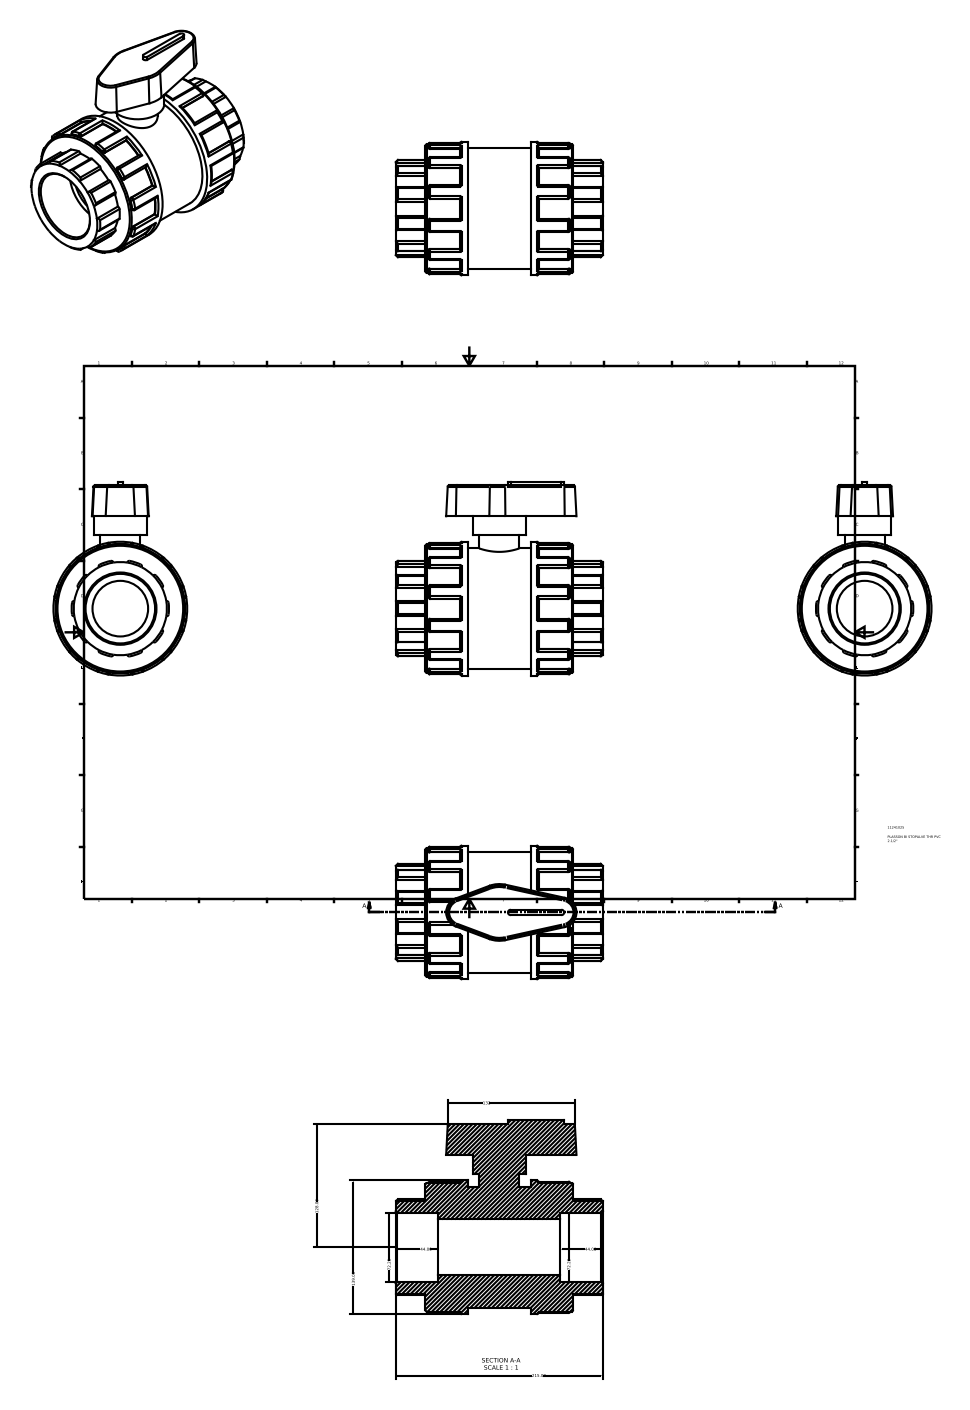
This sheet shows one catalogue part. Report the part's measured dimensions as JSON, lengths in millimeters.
{"part_name": "11241025", "step_written_by": "Autodesk Inventor 2015 (AUTOMOTIVE_DESIGN)", "units": "millimeters", "bodies": {"solids": 1, "faces": 434, "planar": 114, "cylindrical": 192, "other": 128}, "overall_size": [215, 201.34, 139], "volume_mm3": 2102000, "surface_area_mm2": 182297, "round_holes": [[57.78, 1], [72.23, 1]], "round_bosses_or_shafts": [[139, 1], [133.44, 1], [125.1, 1], [55.6, 1], [41.7, 1]], "partial_cylinders_radius": [[2.17, 76], [1.45, 4], [2.78, 2], [48.39, 1], [50.56, 1]], "face_to_face_distances": [30.8, 44, 140.2, 184.2, 74.8, 109.4, 153.4, 32, 171, 13.2]}
